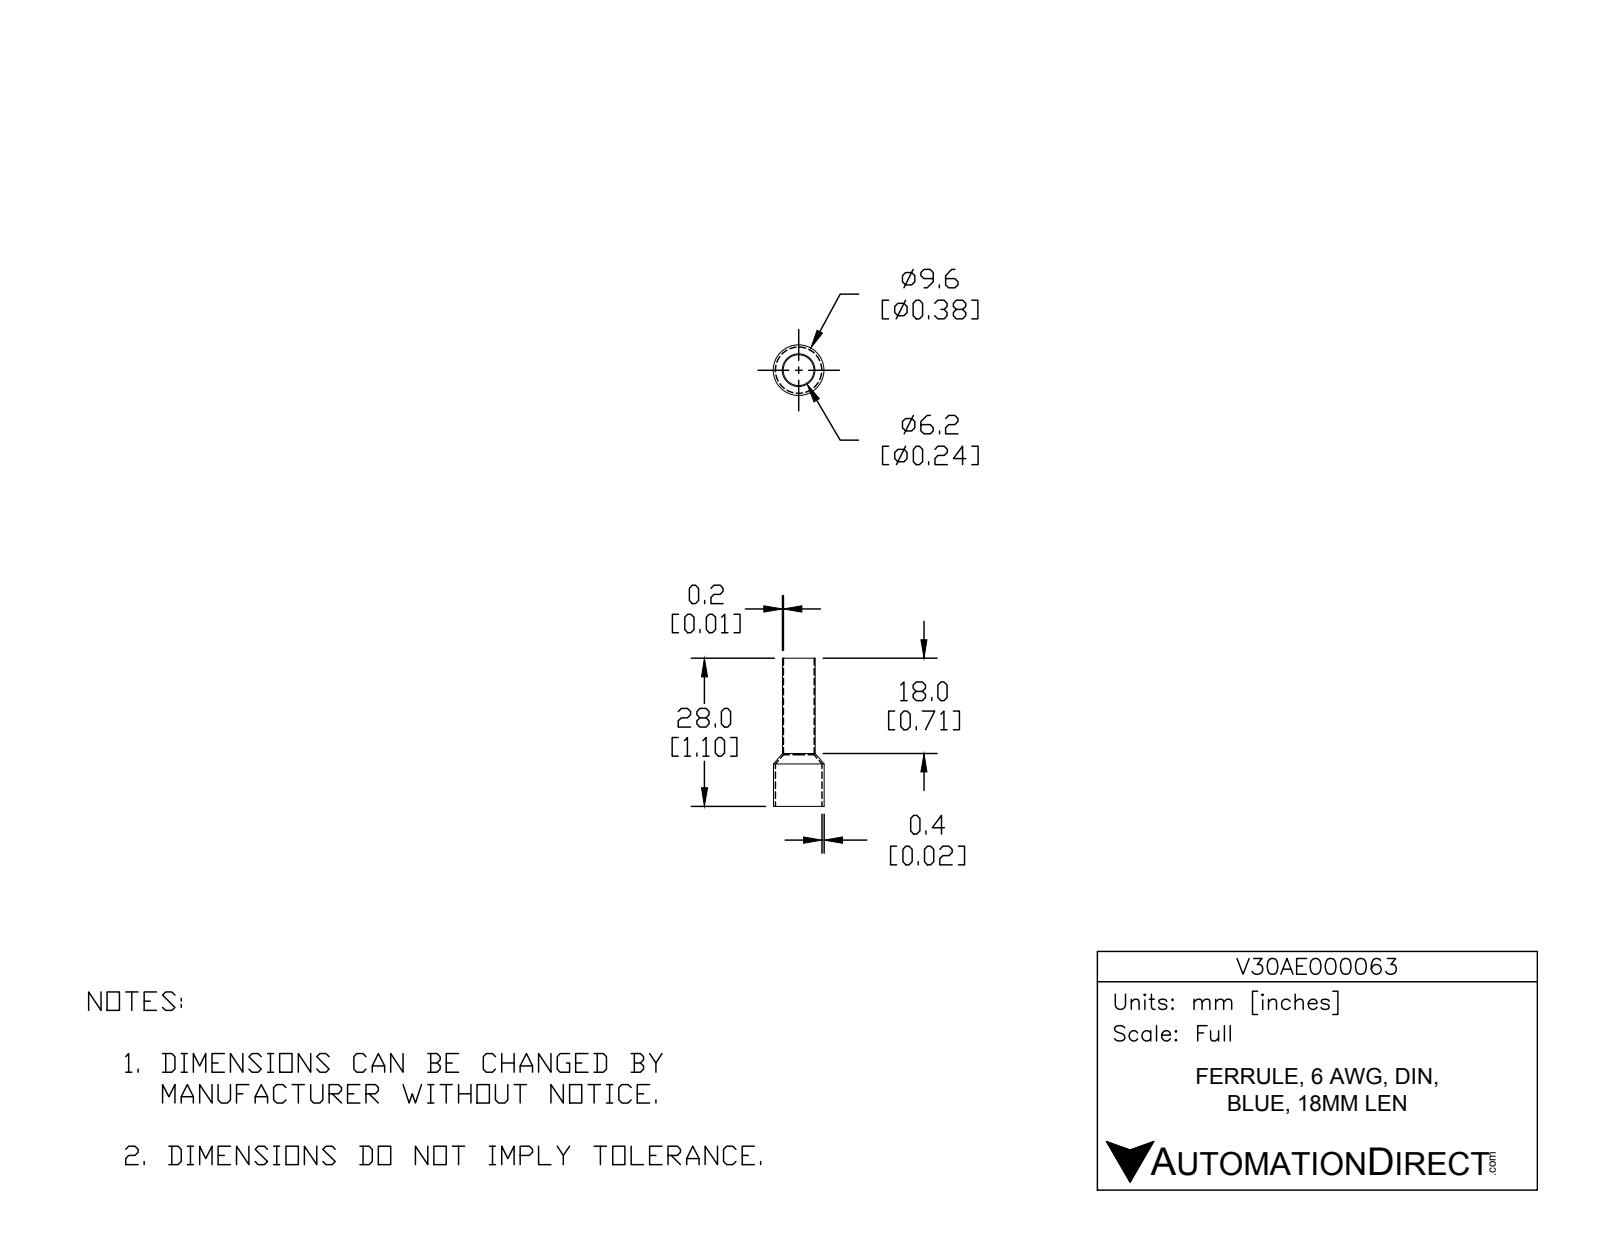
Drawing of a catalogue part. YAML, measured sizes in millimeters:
part_name: "V30AE000063"
step_written_by: "SolidWorks 2017 (AUTOMOTIVE_DESIGN)"
units: millimeters
bodies: {solids: 1, faces: 14, planar: 2, cylindrical: 8, other: 4}
overall_size: [28, 9.6, 9.6]
volume: 179
surface_area: 1279
round_holes:
  - {diameter: 5.8, count: 1}
  - {diameter: 8.8, count: 1}
round_bosses_or_shafts:
  - {diameter: 9.6, count: 1}
  - {diameter: 6.2, count: 1}
face_to_face_distances: [28]
